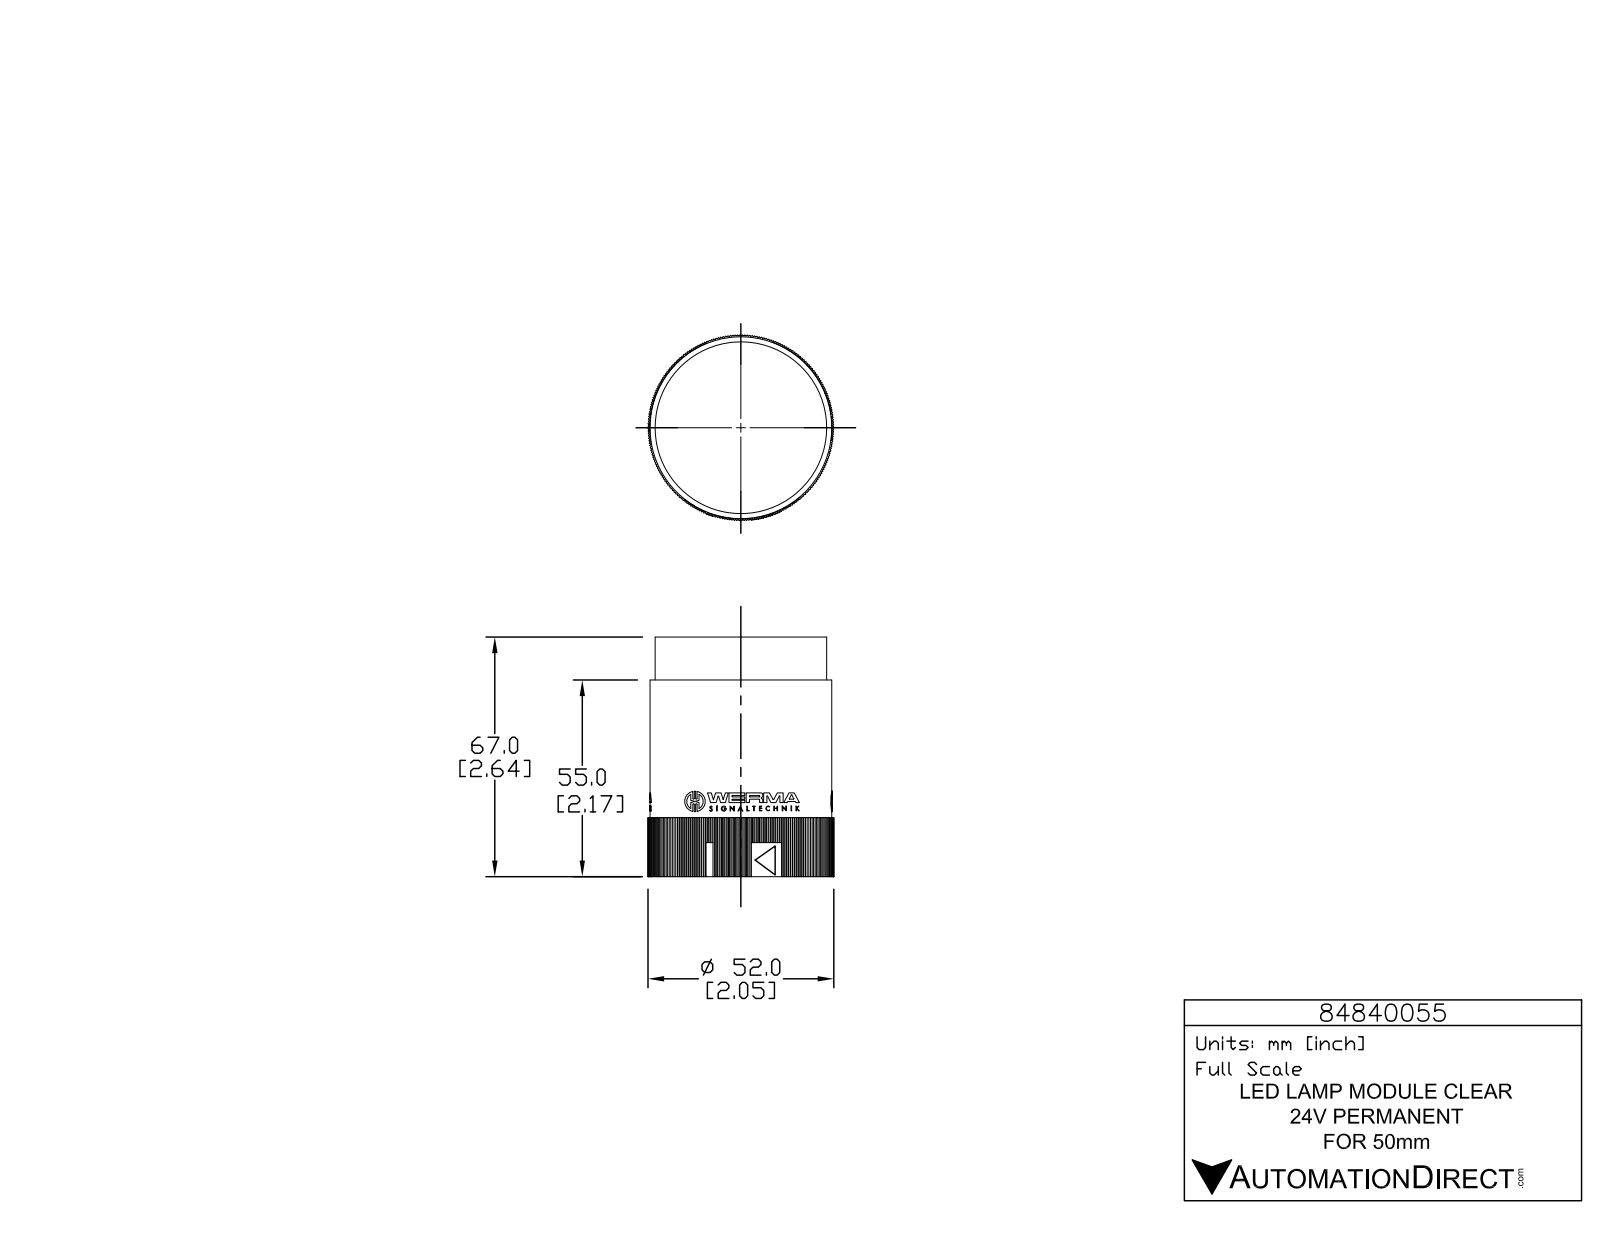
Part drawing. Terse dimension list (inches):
name: 84840055
written by: SolidWorks 2015 (AUTOMOTIVE_DESIGN)
unit: in
bodies: 1 solid, 1265 faces (1020 planar, 245 cylindrical, 0 other)
size: 2.638 × 2.047 × 2.047
volume: 6.873 in³; area: 27.62 in²
holes: 3× ⌀0.039, 1× ⌀1.898
bosses: 3× ⌀0.226, 3× ⌀0.056, 1× ⌀2.002, 1× ⌀1.89
rounds: 6× R0.008, 6× R0.008, 6× R0.008, 6× R0.131, 3× R0.004, 3× R0.005, 3× R0.008, 3× R0.008
face distances: 2.165, 1.428, 1.429, 1.429, 0.472, 2.638, 1.428, 1.428, 1.693, 1.988
